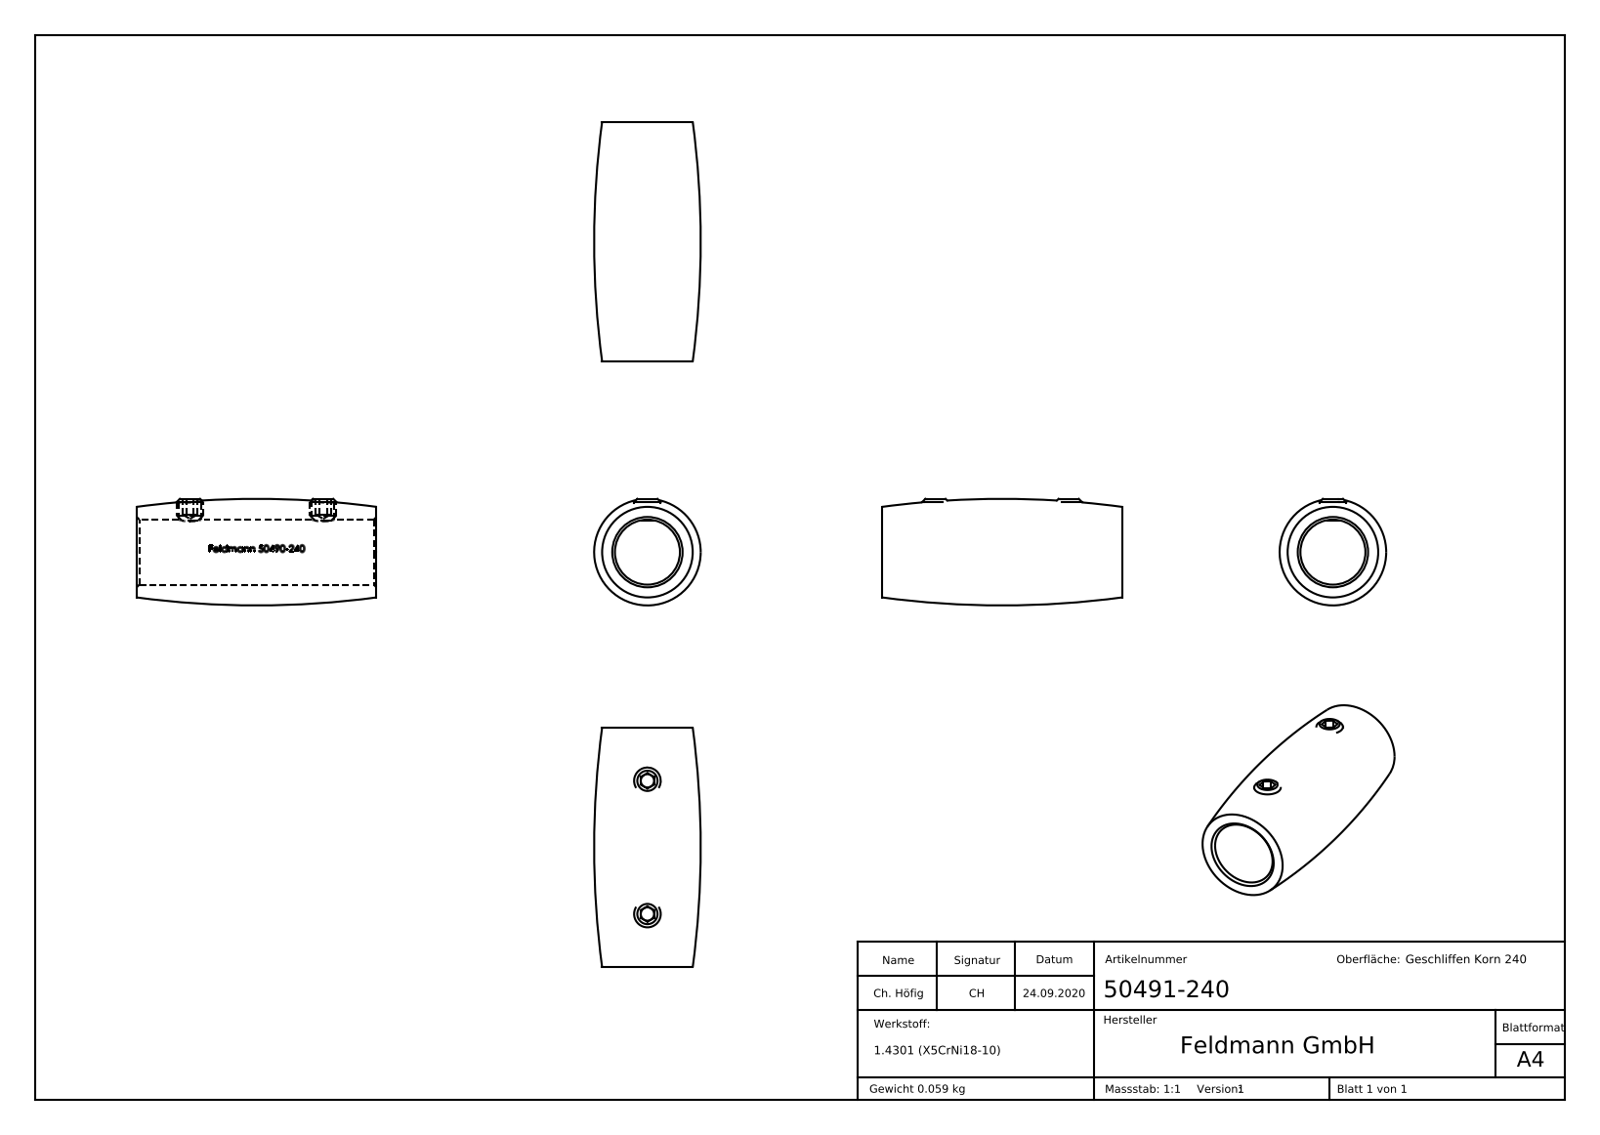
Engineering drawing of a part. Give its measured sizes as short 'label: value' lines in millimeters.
name: 50491-240; DIN913; 5049X-240 Teil1; 5049X-240 Teil1_50491-240 Teil1 (+1 more)
written by: SolidWorks 2018 (CONFIG_CONTROL_DESIGN)
unit: mm
bodies: 3 solids, 287 faces (129 planar, 42 cylindrical, 116 other)
size: 70000 × 4999.89 × 4999.75
volume: 7 528 mm³; area: 4 890 mm²
holes: 2× ⌀4.2, 1× ⌀12.2
bosses: 2× ⌀5
rounds: 1× R6.2
face distances: 45, 21.65, 2.49, 4, 24.14, 19.16, 2.5, 1, 3, 8.68
hole spacings: 25
